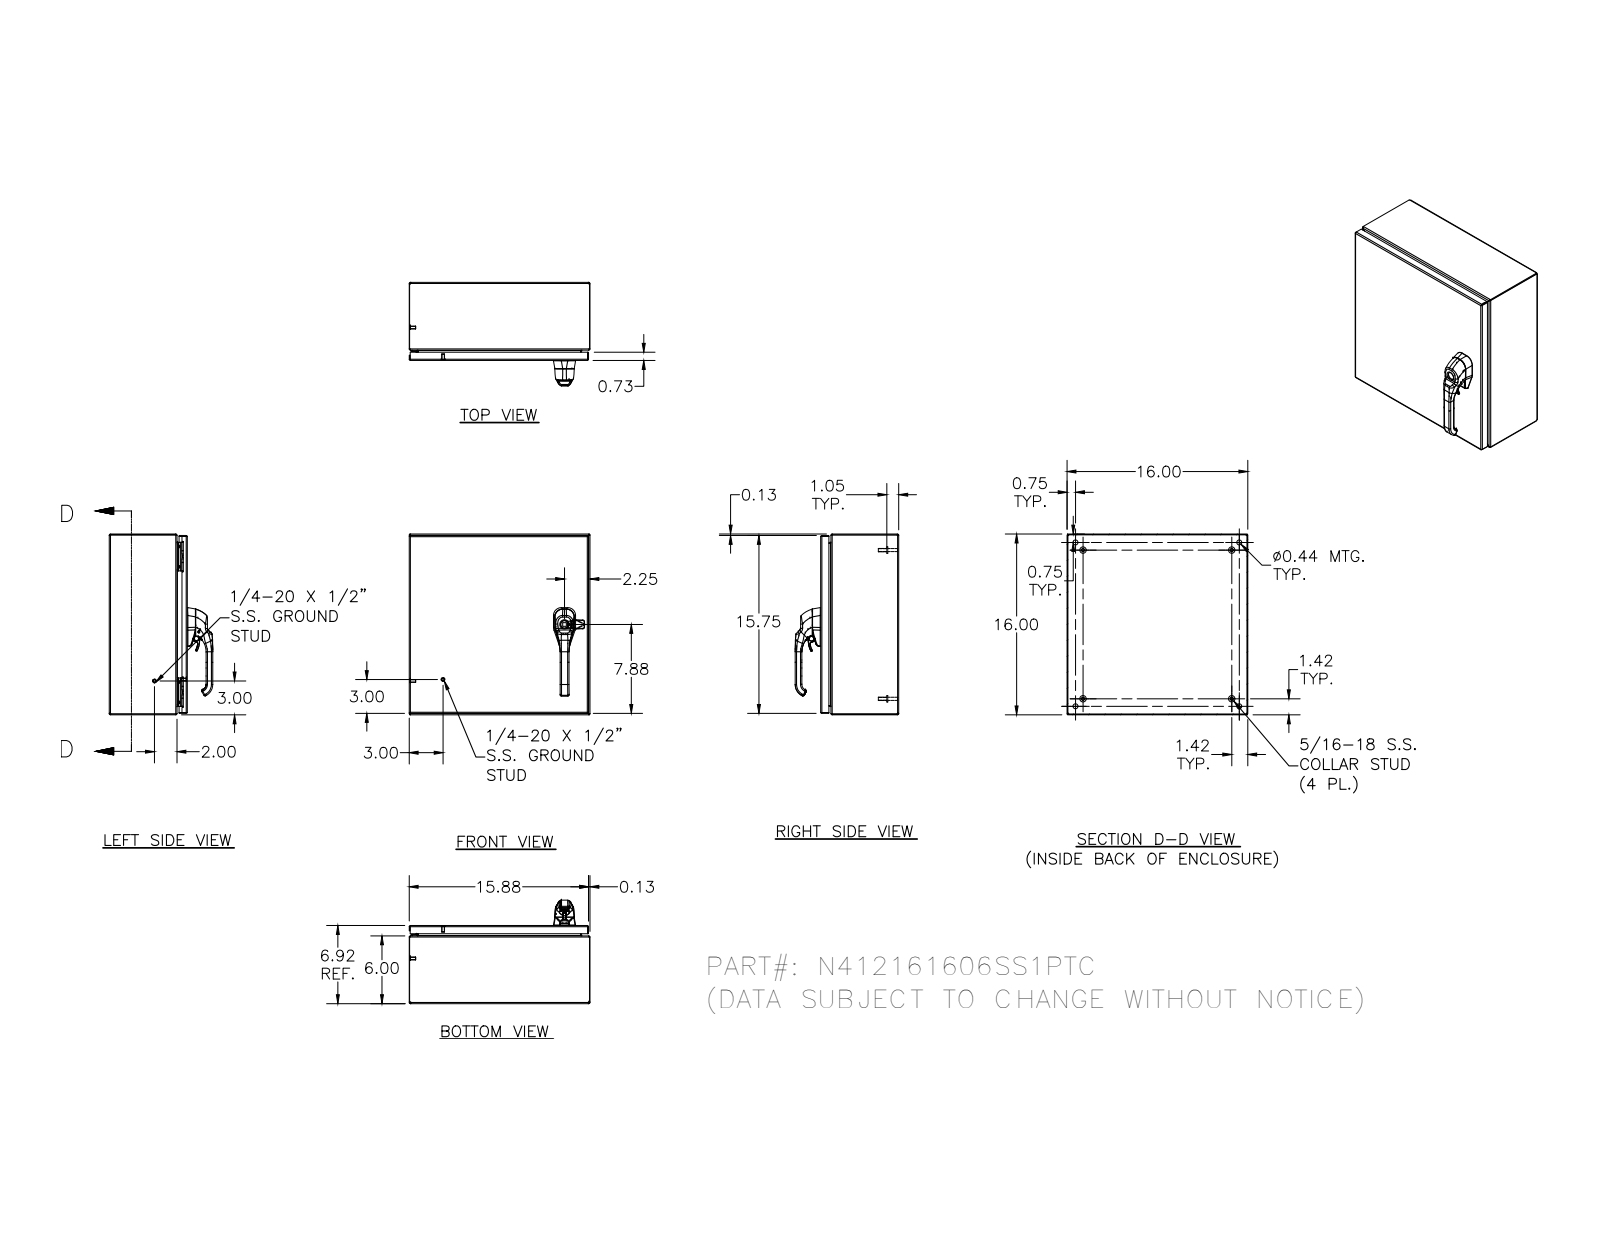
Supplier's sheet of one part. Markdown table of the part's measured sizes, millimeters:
| quantity | value |
| --- | --- |
| part name | N412161606SS1PTC; N412161606SS1PTCBKP; N4121616SS1PTCLID; HFW328176 (+8 more) |
| STEP written by | Autodesk Inventor 2012 (AUTOMOTIVE_DESIGN) |
| units | millimeters |
| bodies | 41 solids, 2782 faces (882 planar, 1035 cylindrical, 865 other) |
| overall size | 406.4 × 406.4 × 232.8 |
| volume | 1 365 000 mm³ |
| surface area | 1 399 000 mm² |
| round holes (diameter × count) | 2.4 × 4, 3.9 × 4, 4.2 × 4, 4.4 × 4, 4.8 × 4, 11.1 × 4, 5.4 × 3, 7.1 × 3, 4 × 2, 8 × 2, 10.2 × 2, 10.5 × 2 |
| round bosses / shafts (diameter × count) | 6.4 × 10, 14.3 × 4, 9.1 × 4, 8.1 × 4, 7.6 × 4, 7 × 4, 6.5 × 4, 4.2 × 4 |
| partial cylindrical surfaces (radius × count) | 0.5 × 173, 0.3 × 101, 0.8 × 30, 1.3 × 26, 0.5 × 21, 2.7 × 20, 0.4 × 18, 2 × 14 |
| main face-to-face distances | 1.9, 173.8, 404.5, 175.7, 171.9, 402.6, 406.4, 150.5, 23.3, 3.2 |
| hole center spacings | 304.7, 368.3, 0.4, 16.8, 321.5, 360.2, 385.4, 0.5 |
